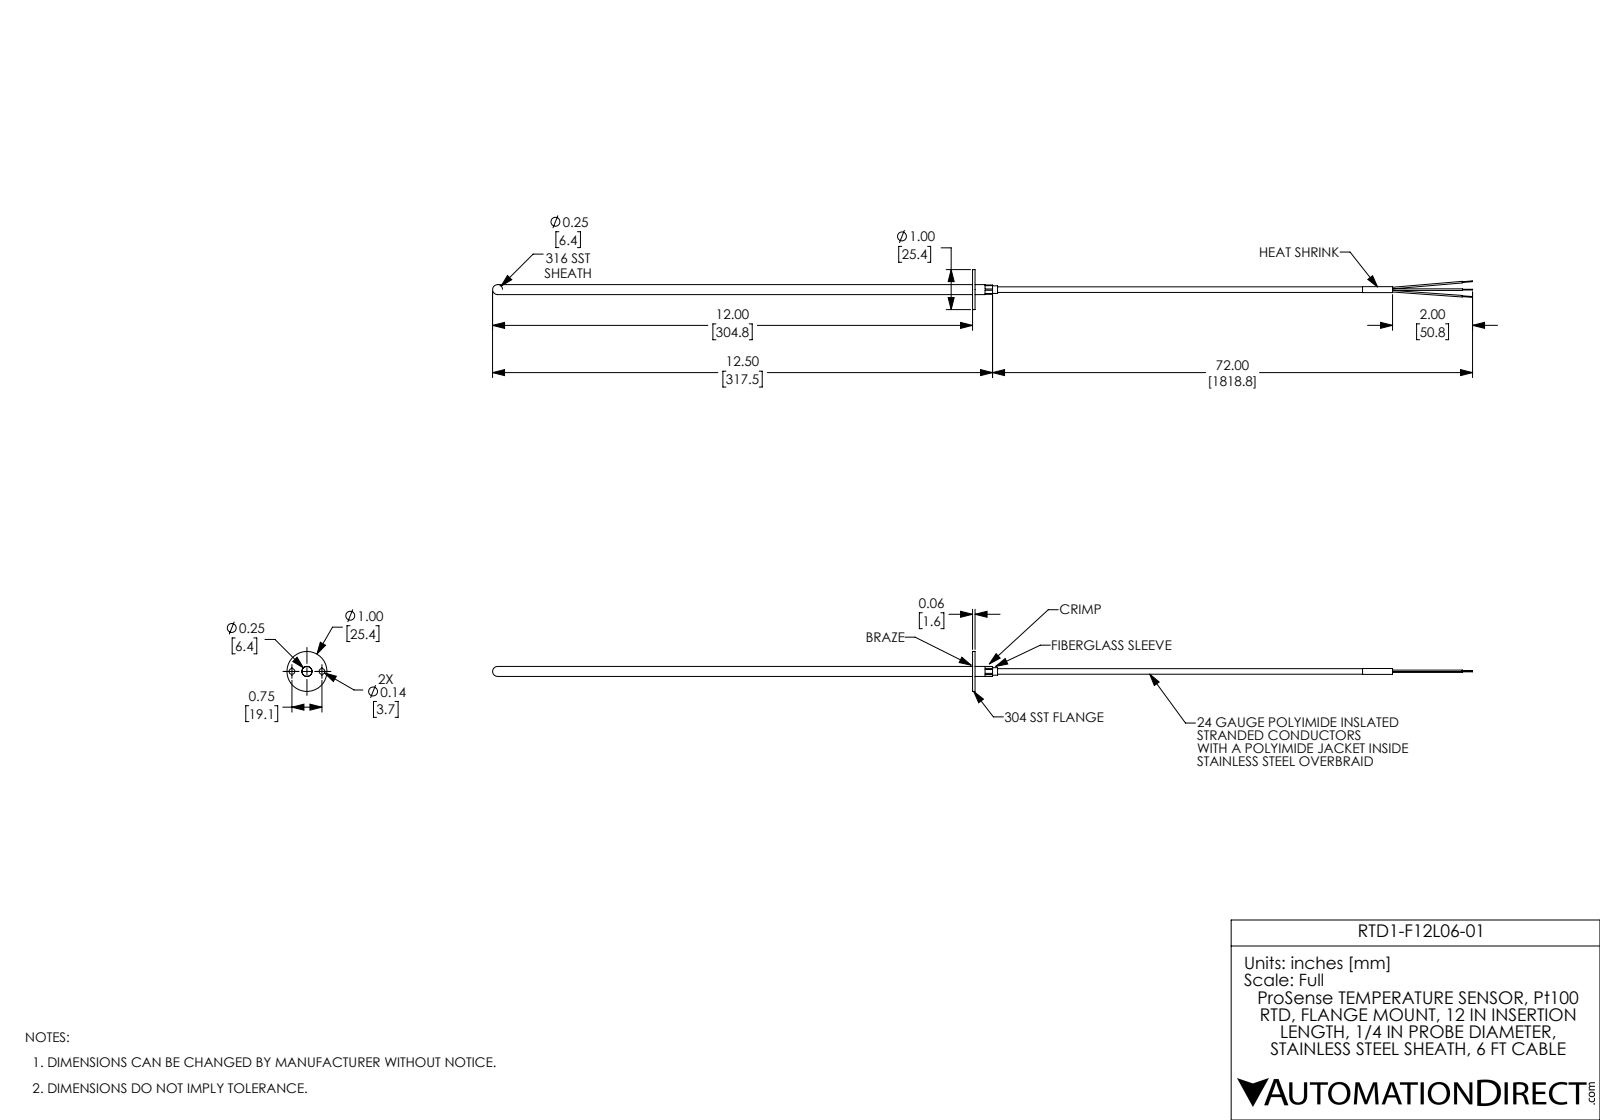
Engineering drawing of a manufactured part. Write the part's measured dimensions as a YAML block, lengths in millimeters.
part_name: "RTD1-F12L06-01"
step_written_by: "SolidWorks 2017 (AUTOMOTIVE_DESIGN)"
units: millimeters
bodies: {solids: 7, faces: 70, planar: 31, cylindrical: 32, other: 7}
overall_size: [622.3, 25.4, 25.4]
volume: 13600
surface_area: 17550
round_holes:
  - {diameter: 3.7, count: 3}
  - {diameter: 3.5, count: 1}
  - {diameter: 4.8, count: 1}
  - {diameter: 6.5, count: 1}
round_bosses_or_shafts:
  - {diameter: 25.4, count: 1}
  - {diameter: 6.4, count: 1}
  - {diameter: 4.8, count: 1}
  - {diameter: 4.8, count: 1}
  - {diameter: 3.8, count: 1}
  - {diameter: 3.6, count: 1}
  - {diameter: 3.4, count: 1}
  - {diameter: 1, count: 1}
face_to_face_distances: [1.6, 12.7, 11.1, 5.9, 19.1, 3.2, 4.8, 15.9, 15.9, 14.3]
hole_center_spacings: [9.5, 9.5, 19.1]
